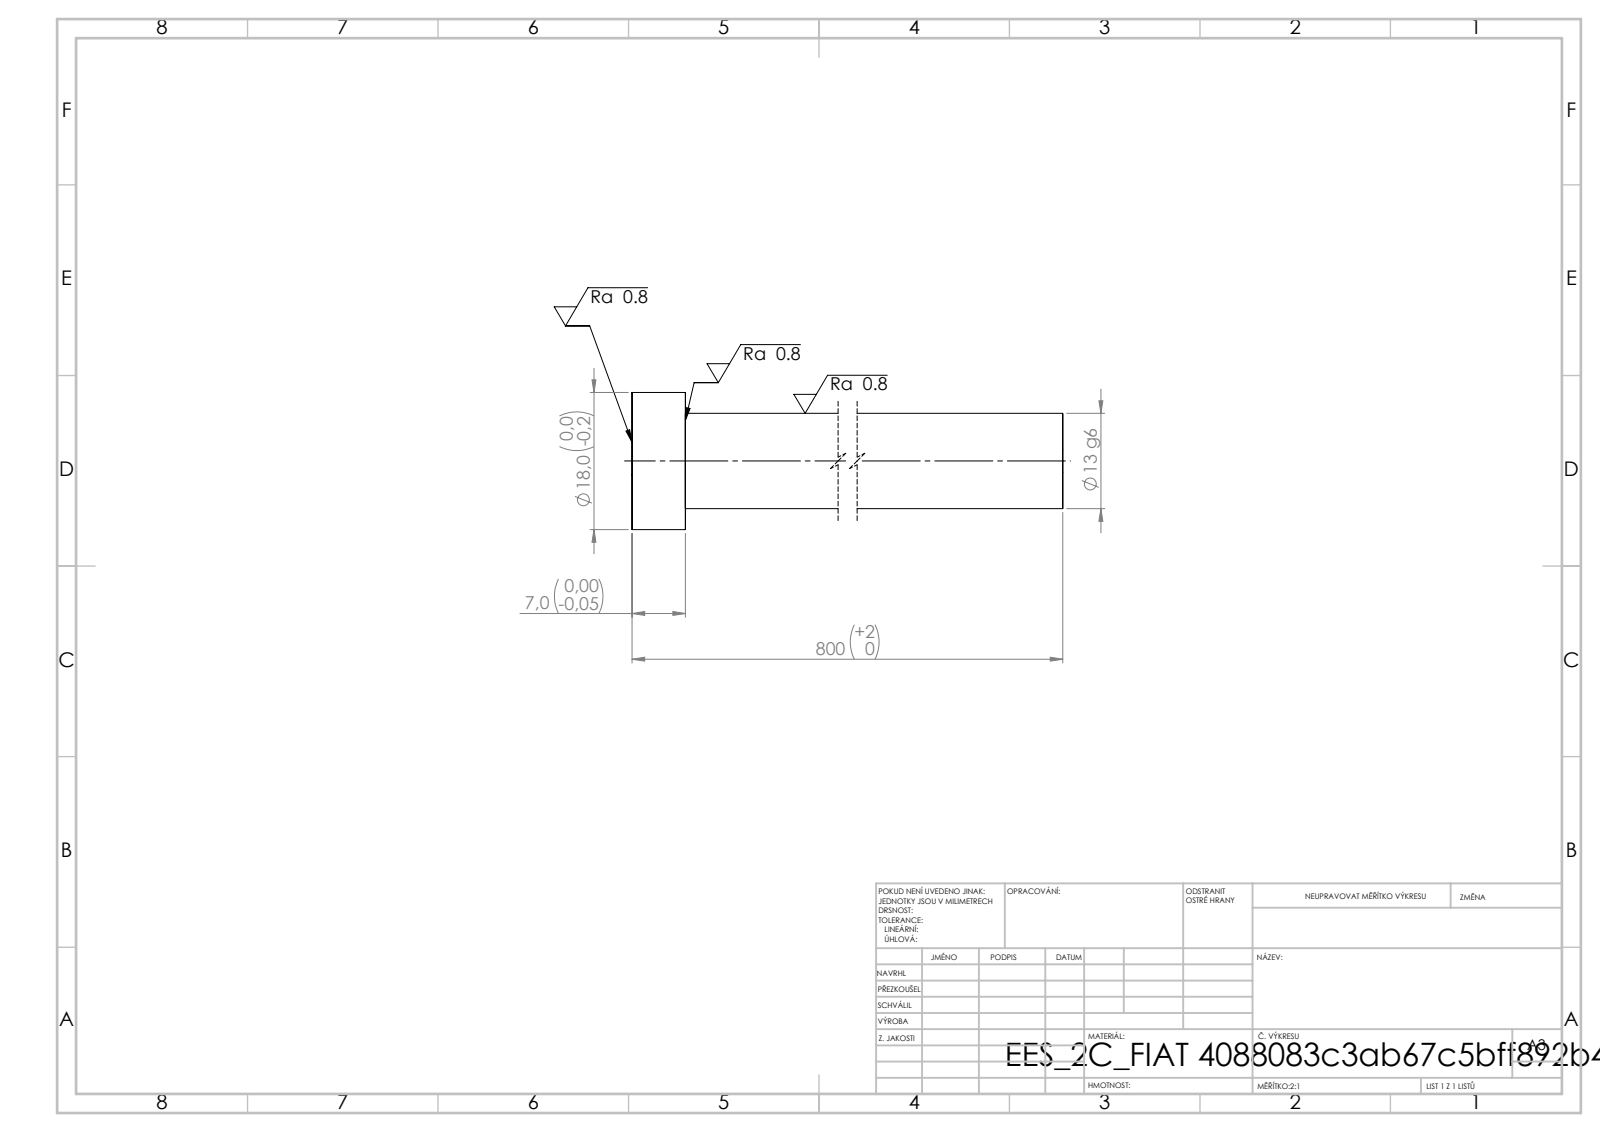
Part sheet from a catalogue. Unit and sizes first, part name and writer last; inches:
Units: inches
Overall size (bounding box): 31.496 × 0.709 × 0.709
Round bosses / shafts (diameter × count): ⌀0.709 ×1, ⌀0.492 ×1
Main face-to-face distances: 0.276, 31.496, 31.22
Volume: 6.047 in³ · Surface area: 49.67 in²
Bodies: 1 solid, 7 faces (3 planar, 4 cylindrical, 0 other)
STEP written by: SolidWorks 2019 (CONFIG_CONTROL_DESIGN)
